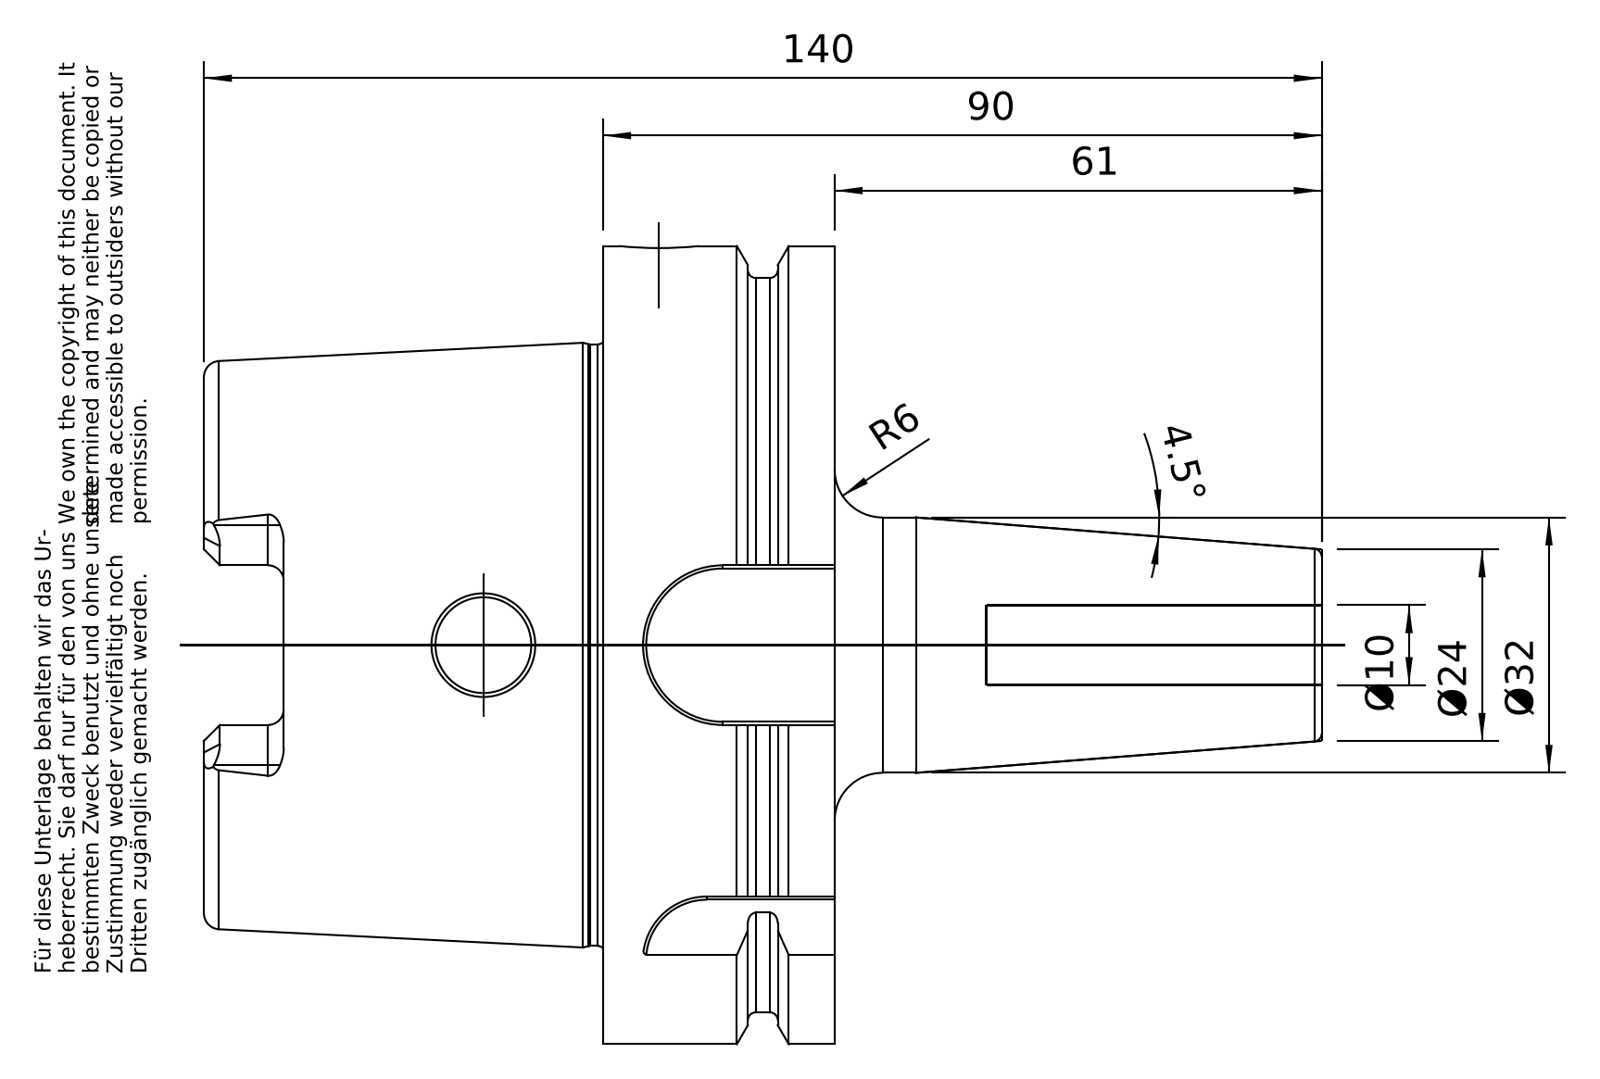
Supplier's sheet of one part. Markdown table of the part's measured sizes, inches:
| quantity | value |
| --- | --- |
| part name | A100-140-10 |
| STEP written by | PRO/ENGINEER BY PARAMETRIC TECHNOLOGY CORPORATION, 2010430 (CONFIG_CONTROL_DESIGN) |
| units | inches |
| bodies | 1 solid, 174 faces (50 planar, 51 cylindrical, 73 other) |
| overall size | 5.512 × 3.937 × 3.937 |
| volume | 17.78 in³ |
| surface area | 87.48 in² |
| round holes (diameter × count) | 0.394 × 2, 0.472 × 1, 0.886 × 1, 0.945 × 1, 0.957 × 1, 0.965 × 1, 2.087 × 1, 2.48 × 1 |
| round bosses / shafts (diameter × count) | 3.937 × 1, 3.622 × 1, 2.967 × 1, 1.26 × 1 |
| partial cylindrical surfaces (radius × count) | 0.079 × 6, 0.197 × 4, 0.315 × 1, 0.394 × 1, 0.433 × 1 |
| main face-to-face distances | 1.142, 0.492, 0.65, 1.969, 2.461, 3.11, 3.465, 3.091, 1.122, 0.63 |
